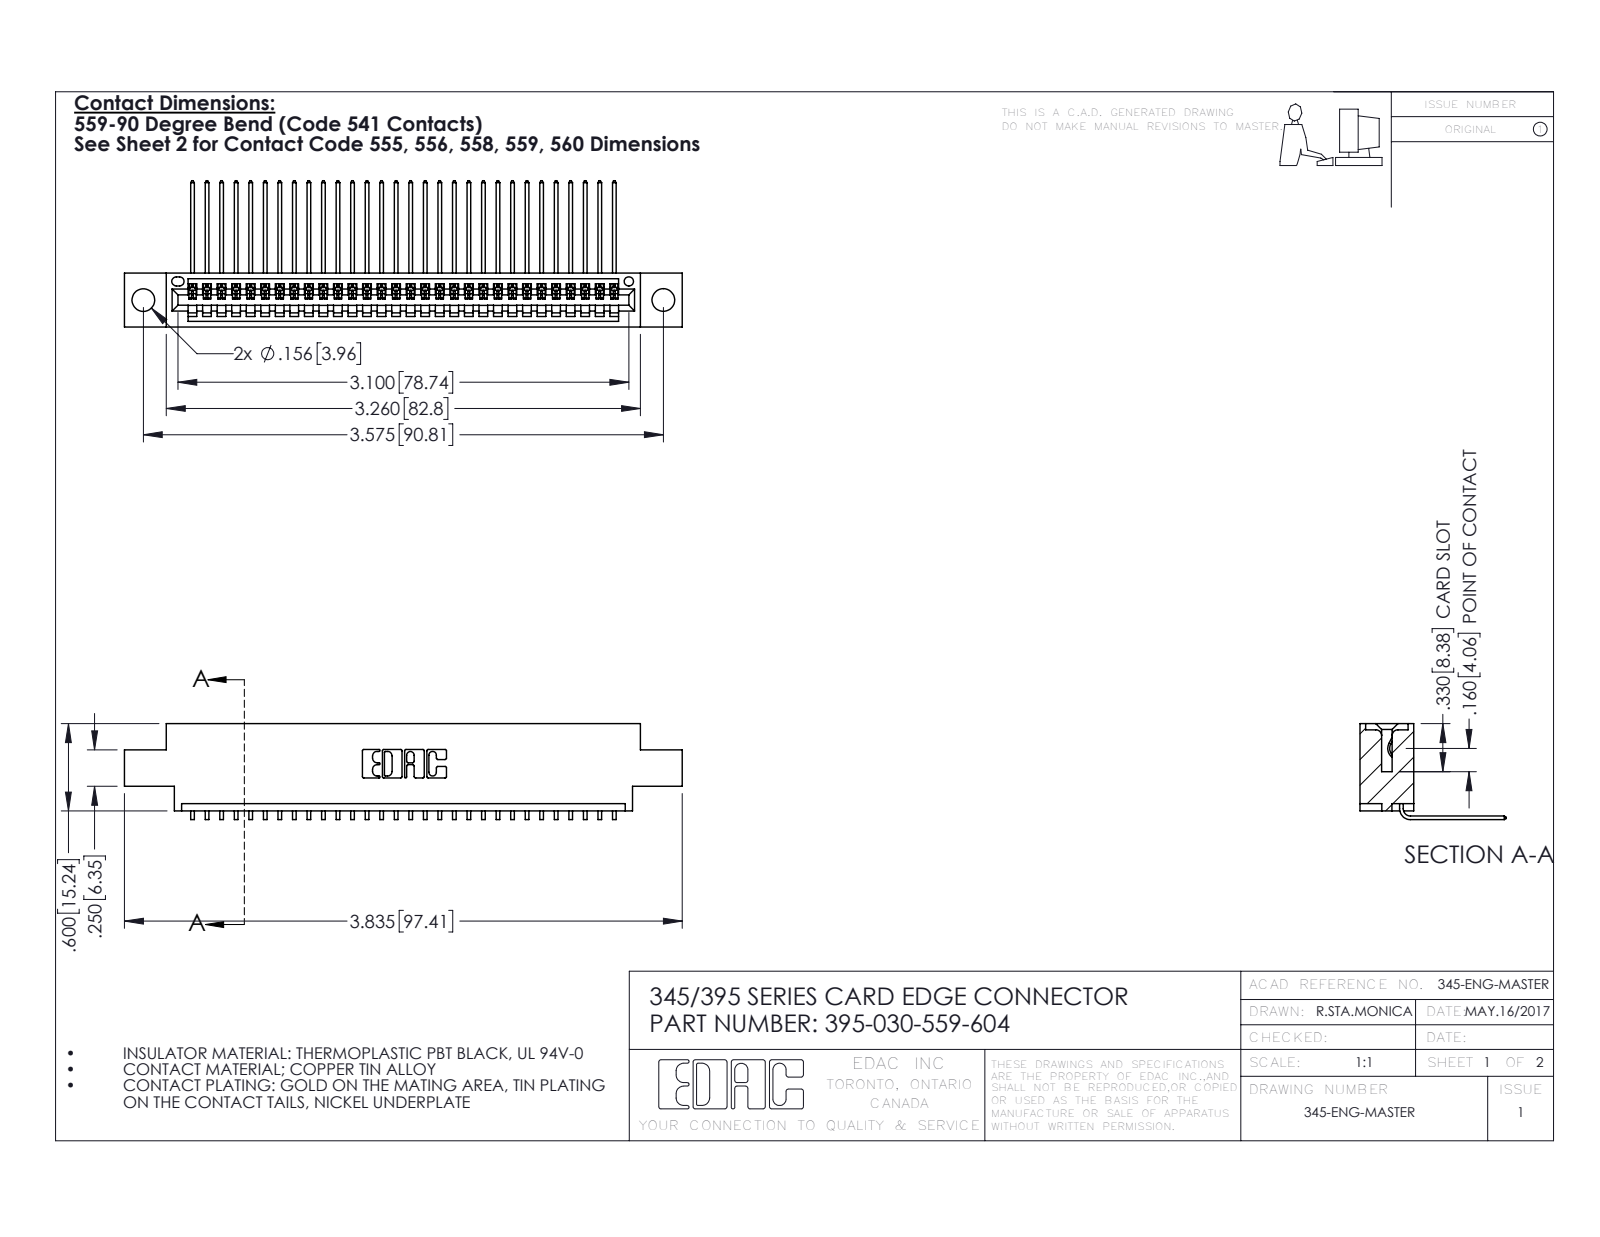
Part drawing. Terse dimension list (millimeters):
name: 395-030-559-604; 345-292-001_558 559 Tail - 1; 345 Part_0.170 Offset - 0.156 Dia-TH
written by: SolidWorks 2016 (CONFIG_CONTROL_DESIGN)
unit: mm
bodies: 31 solids, 1930 faces (1344 planar, 586 cylindrical, 0 other)
size: 97.4 × 25.5 × 16.7
volume: 9 050 mm³; area: 12 390 mm²
holes: 2× ⌀4, 1× ⌀1.6
rounds: 60× R0.2, 22× R0.3, 6× R0.2, 6× R0.8, 3× R0.7, 2× R0.8, 2× R1, 1× R0.4
face distances: 1.8, 7.6, 9.4, 5.1, 2.5, 6.9, 0.6, 5.7, 4.4, 3.8
hole spacings: 6.9, 84.8, 90.8
